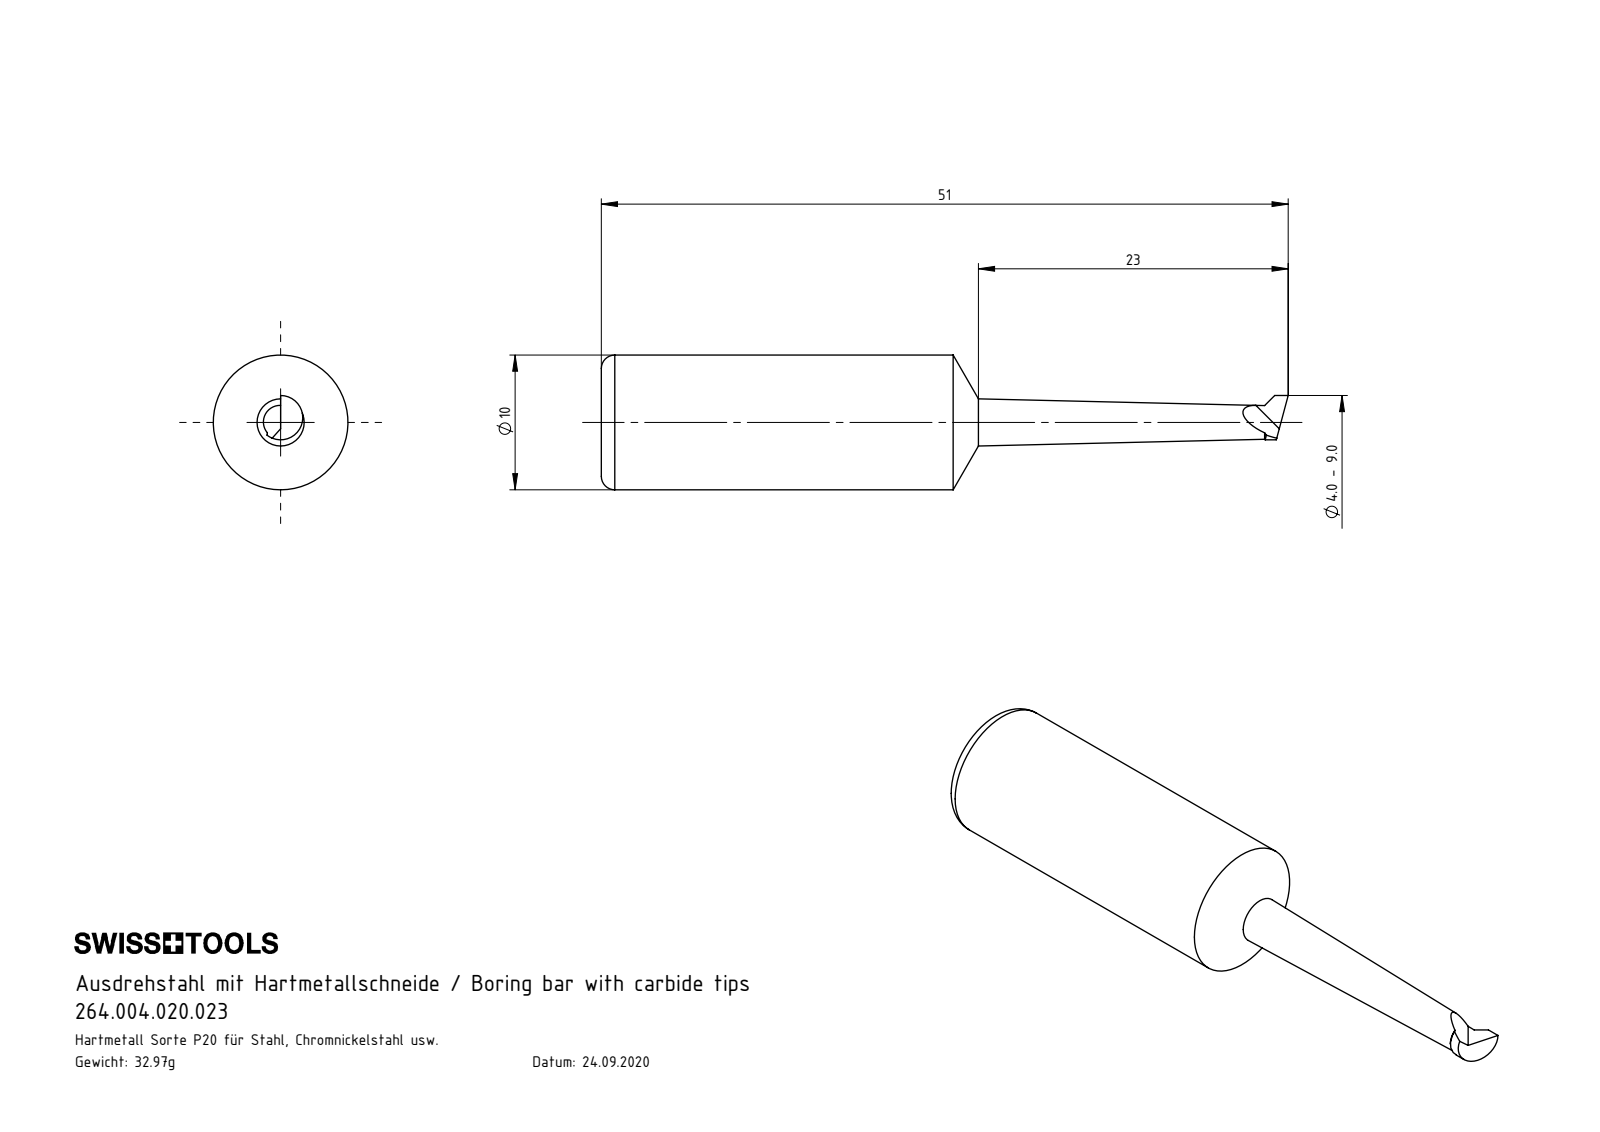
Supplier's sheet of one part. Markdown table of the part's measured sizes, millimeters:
| quantity | value |
| --- | --- |
| part name | U10.B04.002.023 |
| STEP written by | SolidWorks 2017 (AUTOMOTIVE_DESIGN) |
| units | millimeters |
| bodies | 1 solid, 10 faces (4 planar, 2 cylindrical, 4 other) |
| overall size | 51 × 10 × 10 |
| volume | 2 274 mm³ |
| surface area | 1 182 mm² |
| round bosses / shafts (diameter × count) | 10 × 1 |
| partial cylindrical surfaces (radius × count) | 1.65 × 1 |
